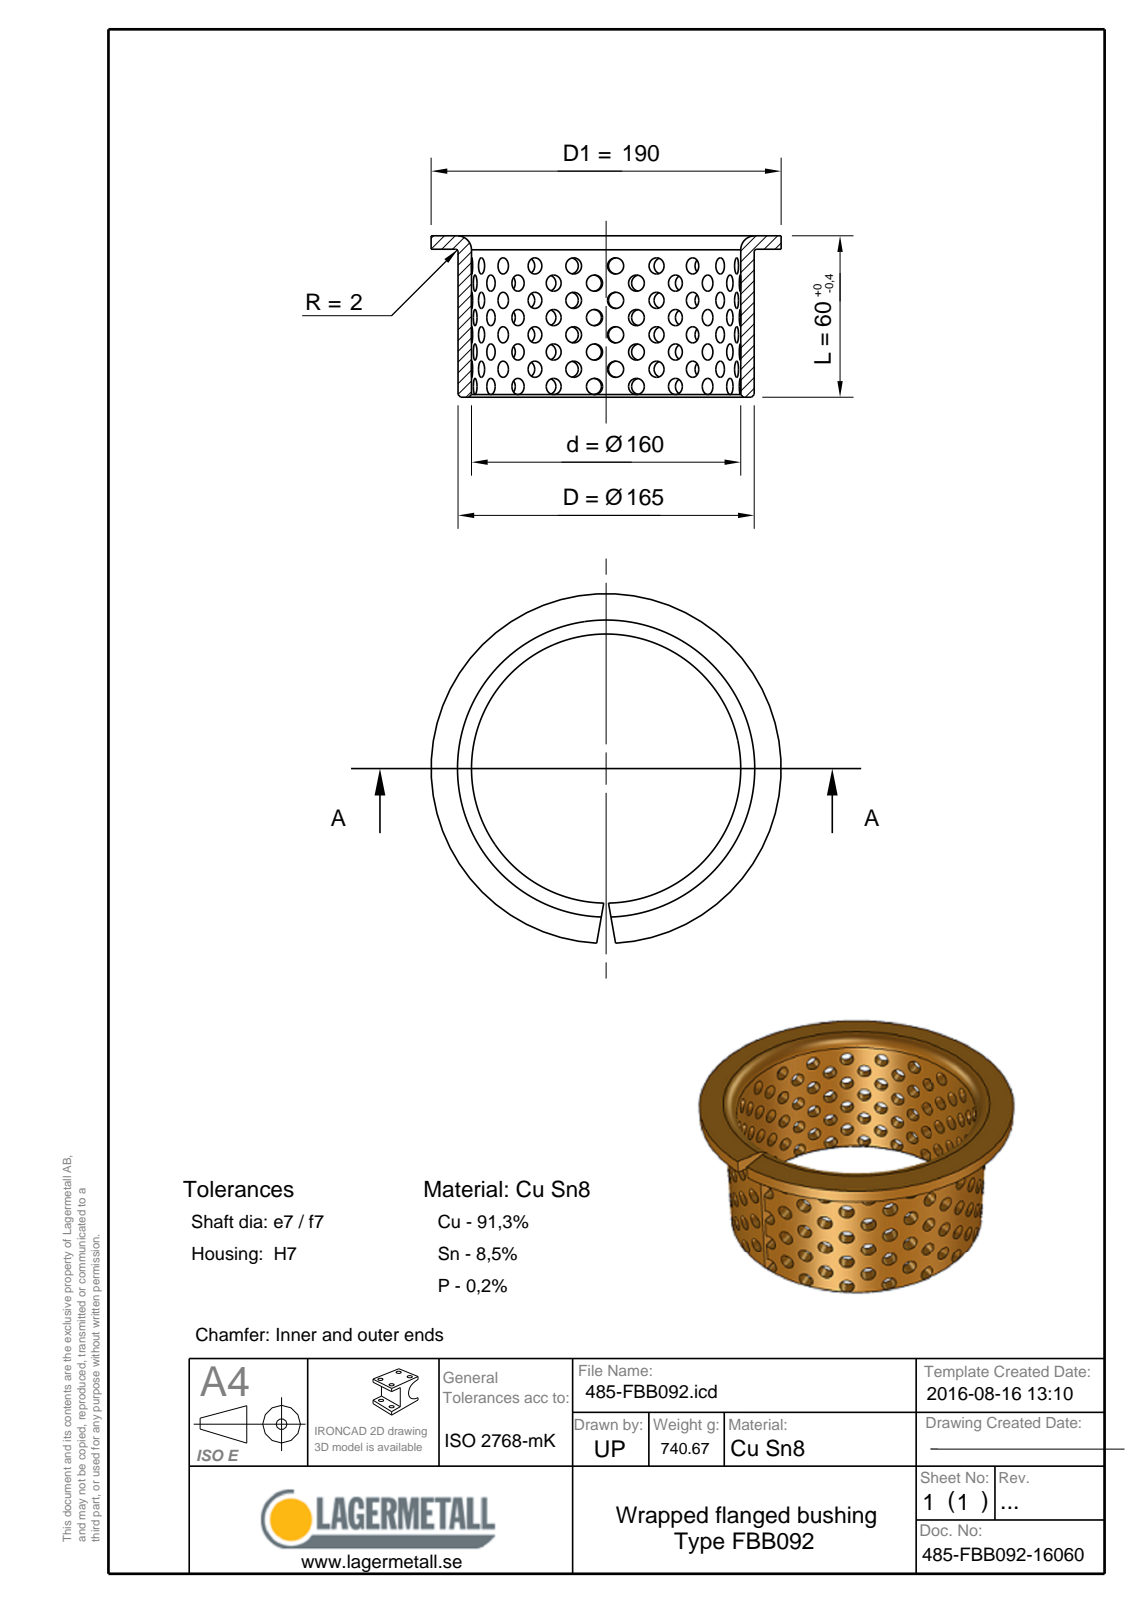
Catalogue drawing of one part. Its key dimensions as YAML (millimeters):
part_name: "485-FBB092-16060"
step_written_by: "Spatial InterOp 3D (CONFIG_CONTROL_DESIGN)"
units: millimeters
bodies: {solids: 1, faces: 12, planar: 5, cylindrical: 3, other: 4}
overall_size: [190, 189.95, 60]
volume: 91440
surface_area: 76115
round_holes:
  - {diameter: 160, count: 1}
round_bosses_or_shafts:
  - {diameter: 190, count: 1}
  - {diameter: 165, count: 1}
face_to_face_distances: [2.5, 57.5, 60]
